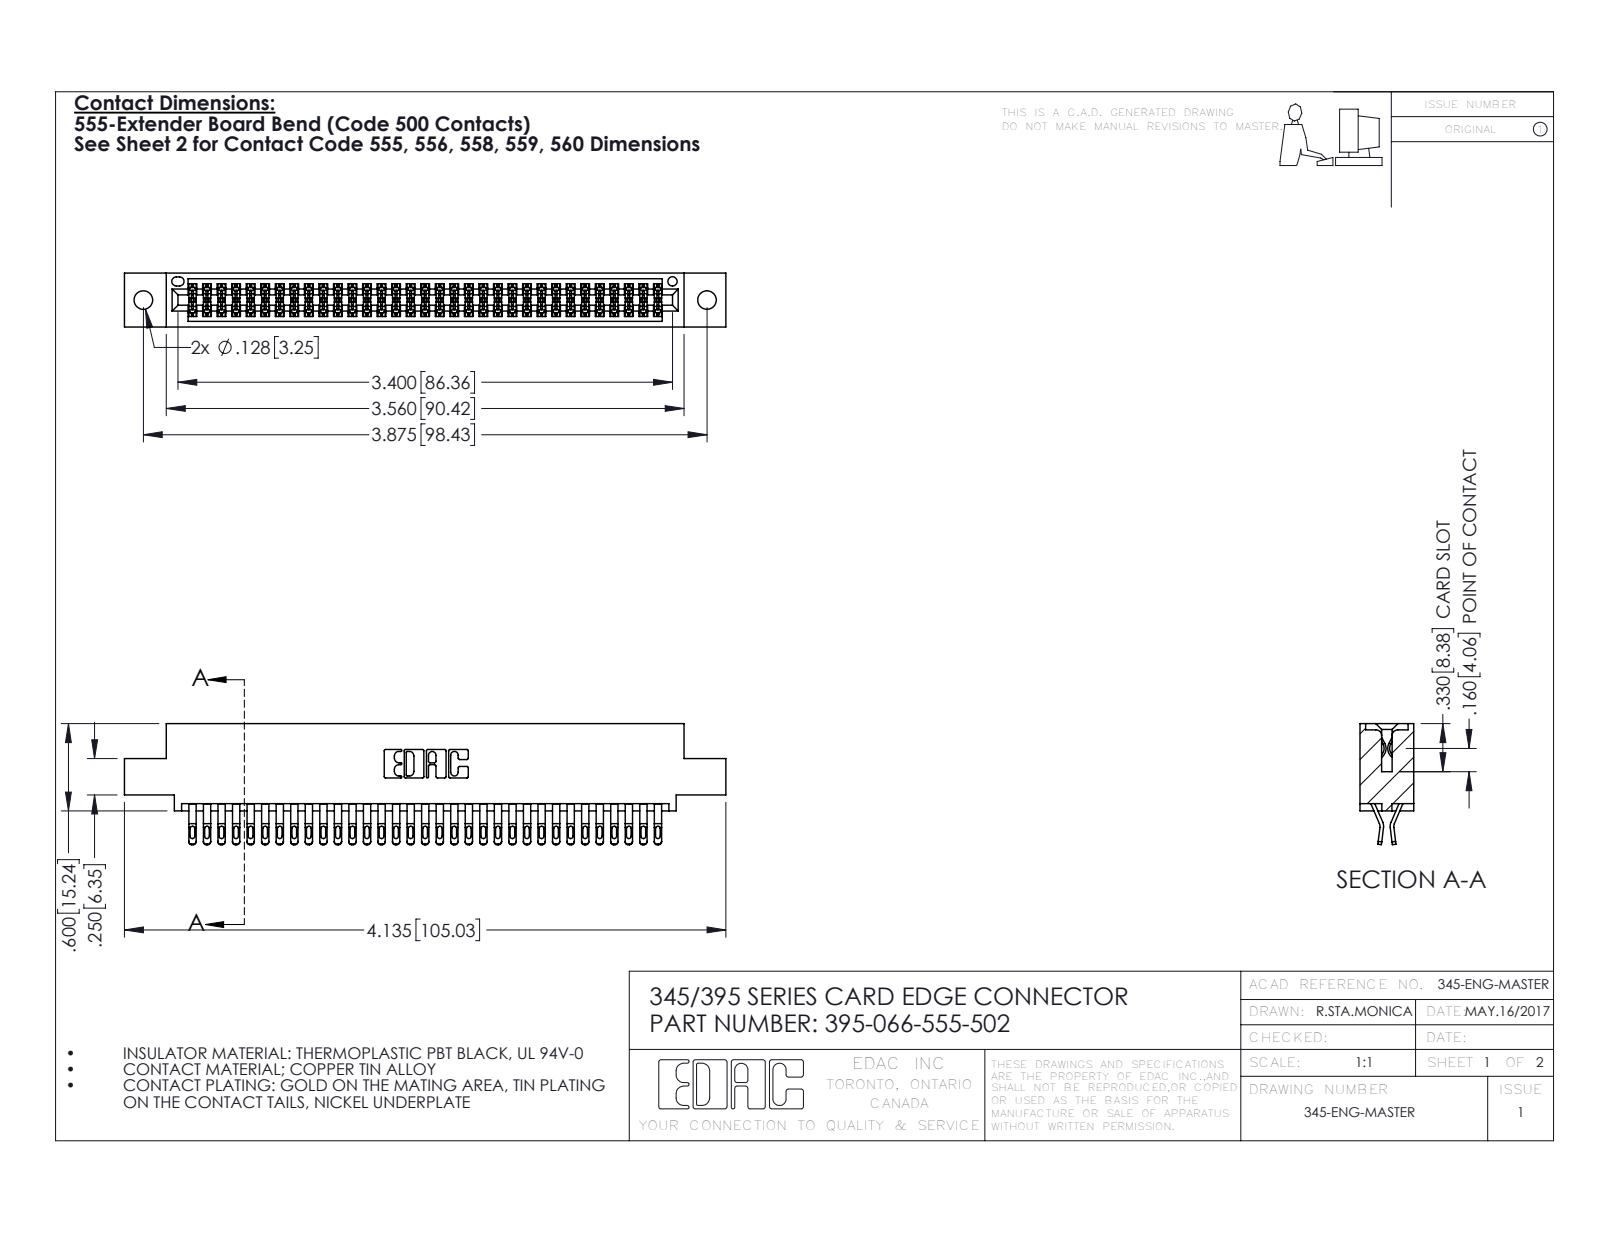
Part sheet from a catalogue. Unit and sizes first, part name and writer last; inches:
Units: inches
Overall size (bounding box): 4.135 × 0.832 × 0.37
Round holes (diameter × count): ⌀0.128 ×2, ⌀0.064 ×1
Partial cylindrical surfaces — rounded edges, fillets, slot ends (radius × count): R0.016 ×165, R0.02 ×132, R0.006 ×99, R0.01 ×22, R0.007 ×6, R0.031 ×6, R0.026 ×3, R0.01 ×2
Main face-to-face distances: 0.298, 0.072, 0.2, 0.37, 0.025, 0.098, 0.272, 0.225, 0.175, 0.149
Hole centre spacings: 0.27, 3.64, 3.875
Volume: 0.622 in³ · Surface area: 23.85 in²
Bodies: 67 solids, 3826 faces (2130 planar, 1696 cylindrical, 0 other)
Part name (STEP PRODUCT): 345 Part_0.110 Offset - 0.128 Dia; 345-292-001_555 Tail; 395-066-555-502
STEP written by: SolidWorks 2016 (CONFIG_CONTROL_DESIGN)
